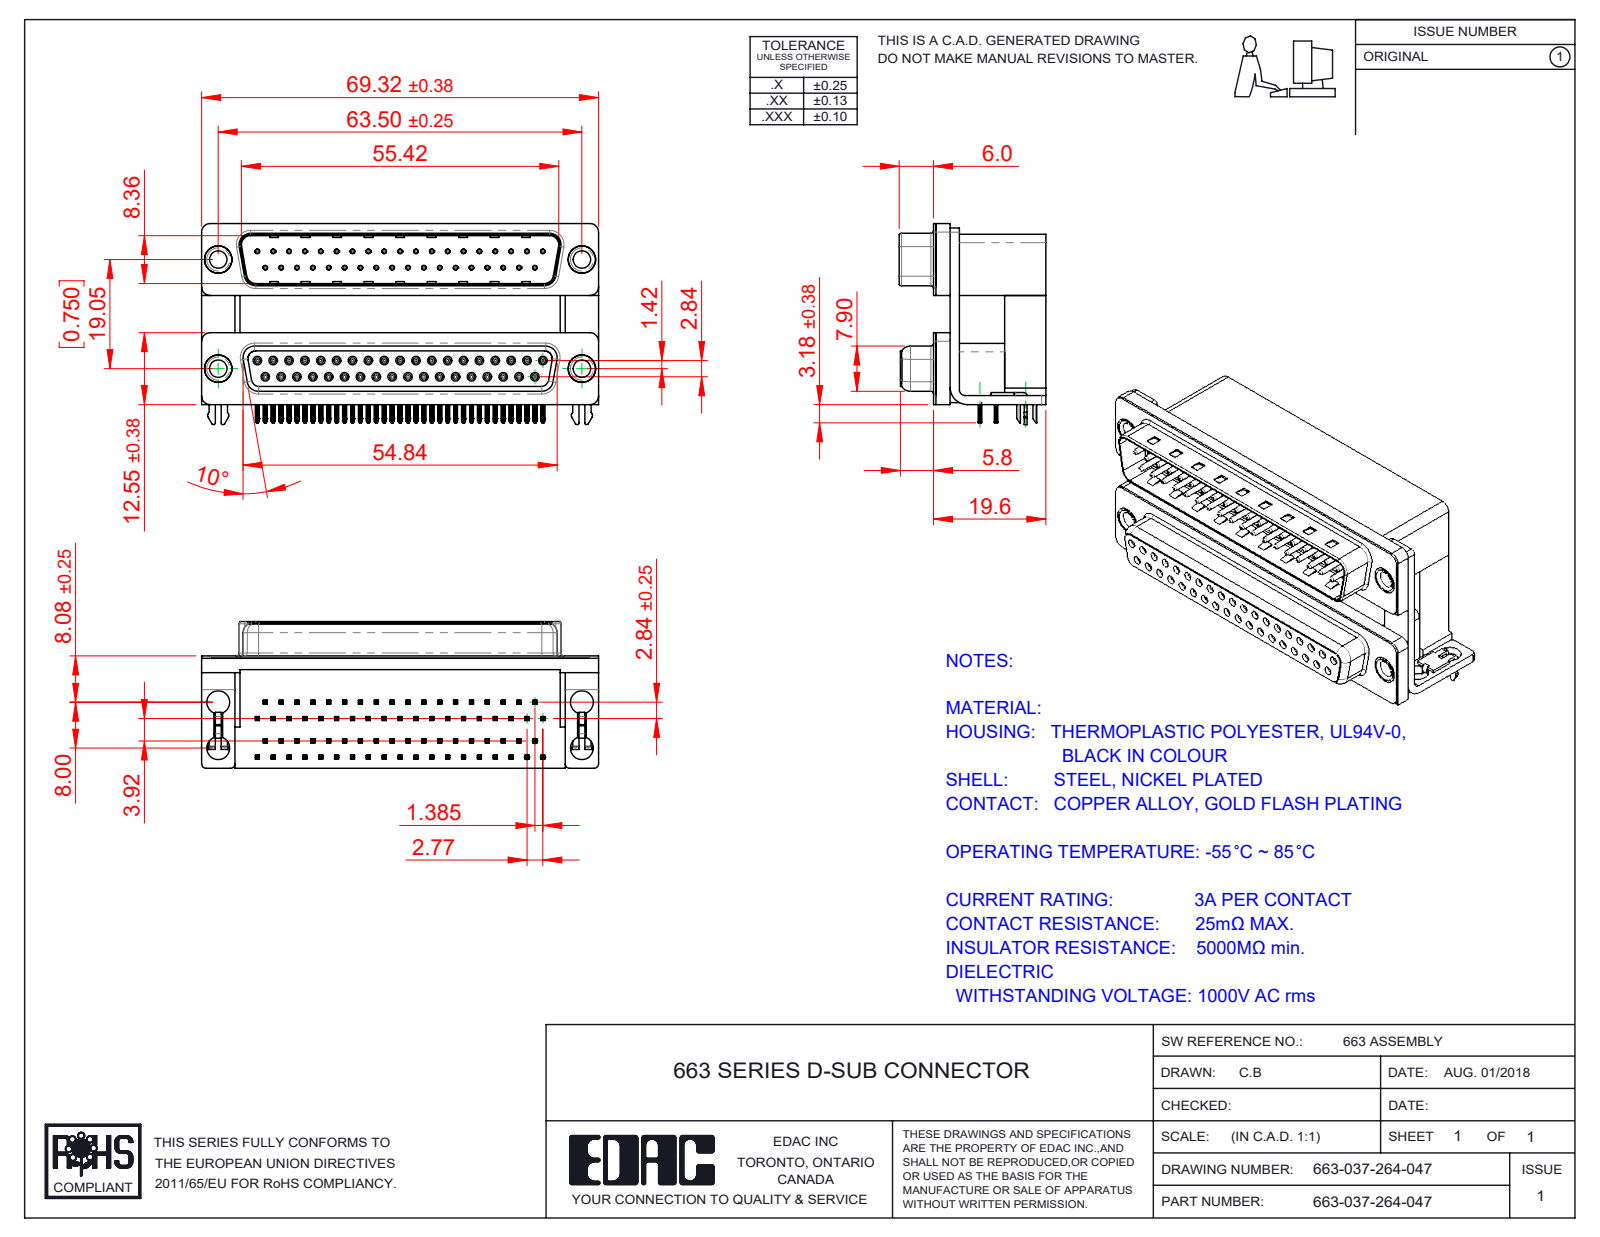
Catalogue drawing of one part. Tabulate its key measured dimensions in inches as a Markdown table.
| quantity | value |
| --- | --- |
| part name | 663-037-264-047; 663 Contact Bottom Upper_M; 663 2 Prong Board Lock_4; 663 Contact Top Lower (+8 more) |
| STEP written by | SolidWorks 2020 (CONFIG_CONTROL_DESIGN) |
| units | inches |
| bodies | 87 solids, 8969 faces (4819 planar, 2171 cylindrical, 1979 other) |
| overall size | 2.729 × 1.382 × 1.008 |
| volume | 1.903 in³ |
| surface area | 50.38 in² |
| round holes (diameter × count) | 0.031 × 74, 0.014 × 37, 0.035 × 37, 0.157 × 8, 0.12 × 4, 0.138 × 4, 0.189 × 4, 0.197 × 4 |
| round bosses / shafts (diameter × count) | 0.047 × 37, 0.03 × 37, 0.193 × 4, 0.187 × 4, 0.152 × 4 |
| partial cylindrical surfaces (radius × count) | 0.004 × 297, 0.01 × 154, 0.006 × 148, 0.005 × 74, 0.014 × 74, 0.013 × 37, 0.011 × 18, 0.02 × 16 |
| main face-to-face distances | 0.756, 0.016, 0.283, 0.472, 0.421, 0.736, 1.157, 0.75, 0.112, 0.657 |
| hole center spacings | 0.124, 0.109, 0.218, 0.327, 0.436, 0.545, 0.654, 0.763 |
